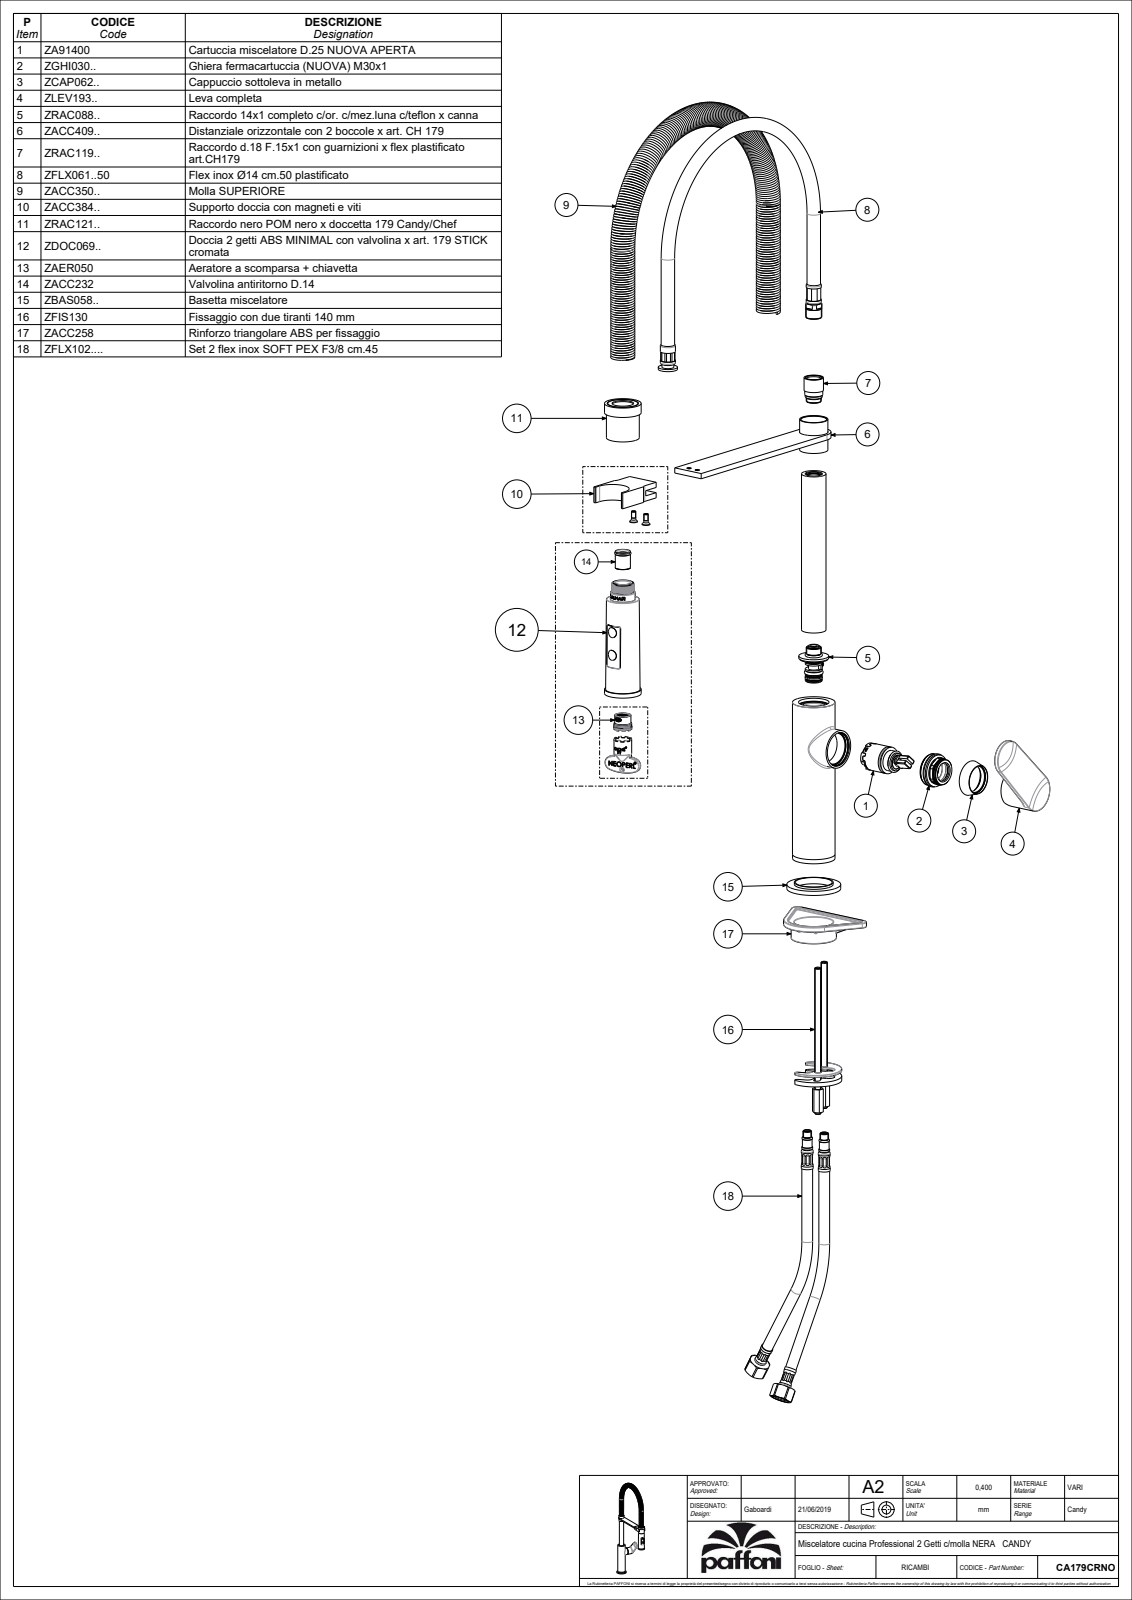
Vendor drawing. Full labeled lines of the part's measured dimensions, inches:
Part name (STEP PRODUCT): CA179CR
STEP written by: CREO PARAMETRIC BY PTC INC, 2020044 (CONFIG_CONTROL_DESIGN)
Units: inches
Bodies: 2 solids, 468 faces (101 planar, 132 cylindrical, 235 other)
Overall size (bounding box): 20.872 × 9.921 × 3.438
Volume: 24.48 in³ · Surface area: 302.3 in²
Round holes (diameter × count): ⌀0.118 ×2, ⌀0.126 ×2, ⌀0.197 ×2, ⌀0.217 ×2, ⌀0.276 ×2, ⌀0.339 ×2, ⌀0.37 ×2, ⌀0.157 ×1, ⌀0.177 ×1, ⌀0.236 ×1, ⌀0.63 ×1, ⌀0.709 ×1
Round bosses / shafts (diameter × count): ⌀0.394 ×2, ⌀0.299 ×2, ⌀0.217 ×2, ⌀1.969 ×1, ⌀1.555 ×1, ⌀1.551 ×1, ⌀1.417 ×1, ⌀1.398 ×1
Partial cylindrical surfaces — rounded edges, fillets, slot ends (radius × count): R0.118 ×4, R0.02 ×2, R0.197 ×2, R0.63 ×2, R0.138 ×1, R0.61 ×1, R0.638 ×1
Main face-to-face distances: 0.197, 0.394, 11.957, 12.154, 6.061, 0.591, 11.76, 12.35, 1.26, 6.709
Hole centre spacings: 0.265, 0.352, 0.368, 0.513, 0.609, 0.374, 0.406, 0.414
